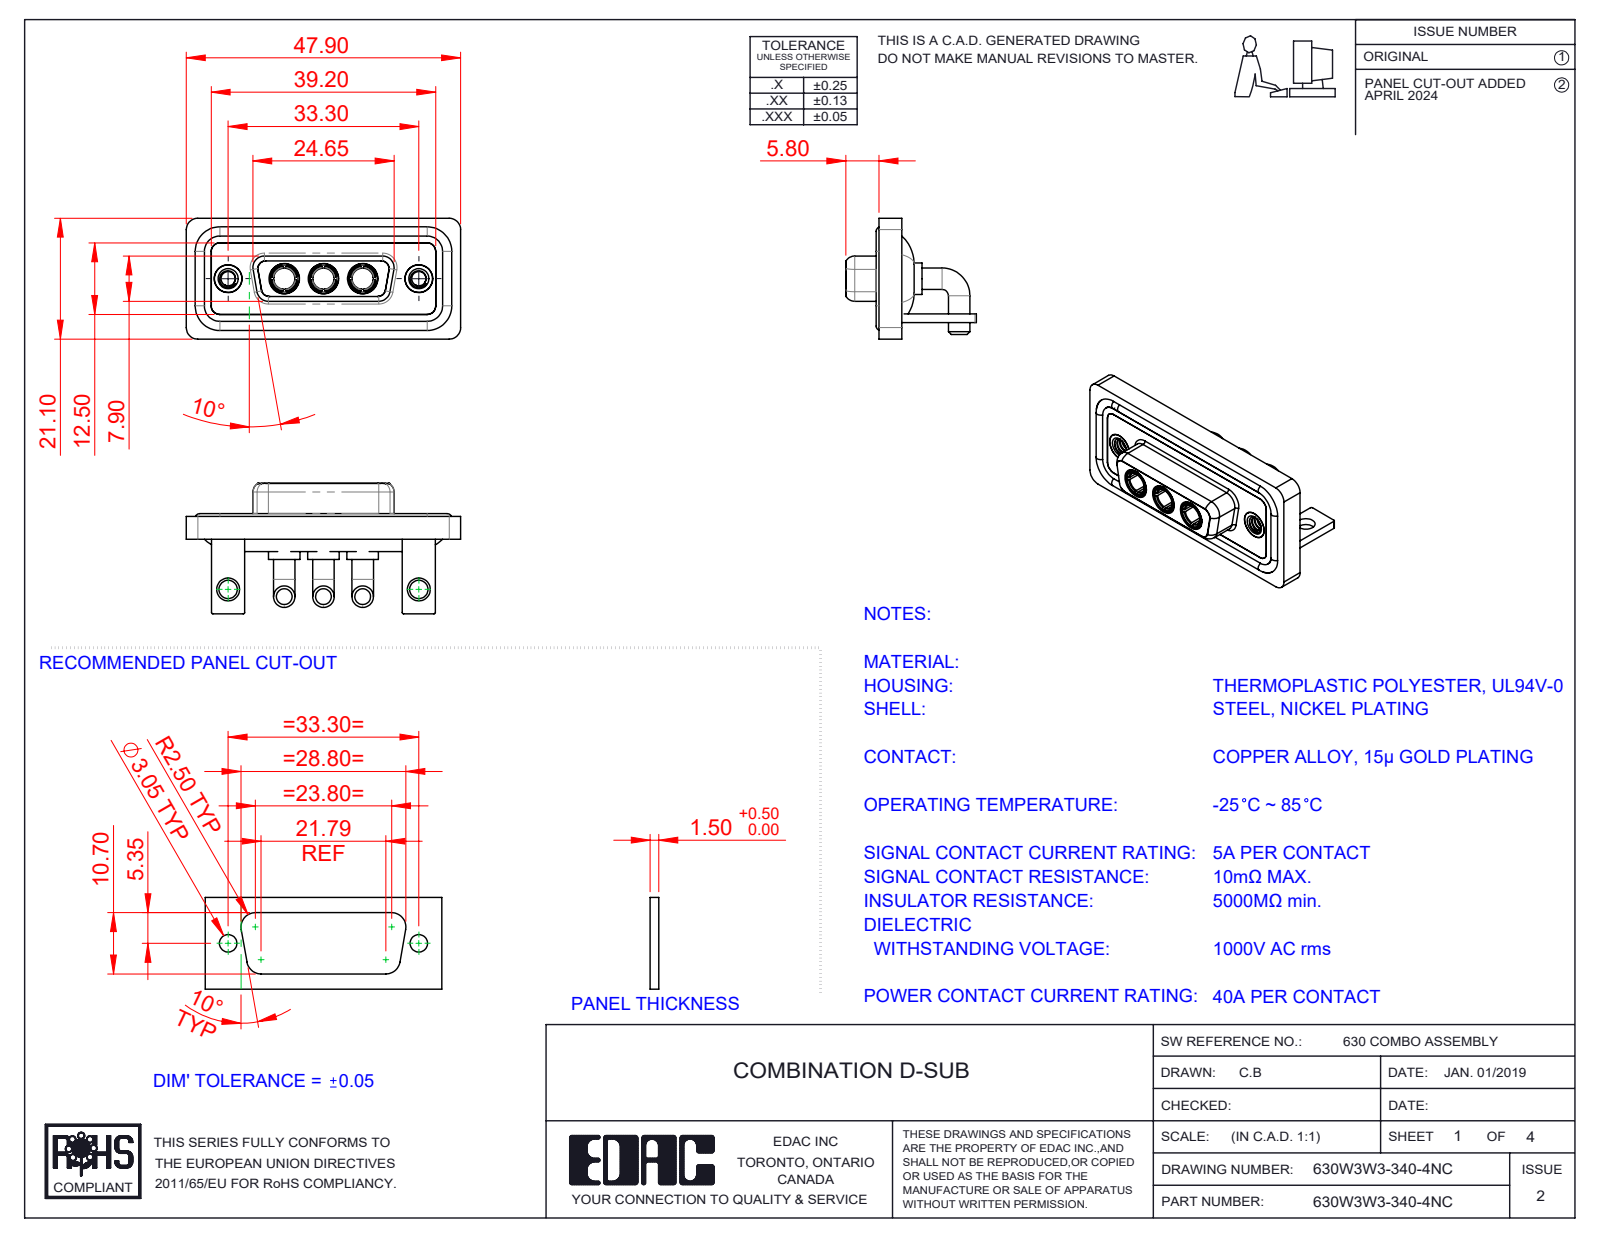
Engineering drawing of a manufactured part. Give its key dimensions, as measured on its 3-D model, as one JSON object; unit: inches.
{"part_name": "630Combo Housing_3W3; 630Combo Threaded Rivet_A; Power Socket_40A RA; 630W3W3-340-4NC (+4 more)", "step_written_by": "SolidWorks 2023 (CONFIG_CONTROL_DESIGN)", "units": "inches", "bodies": {"solids": 15, "faces": 662, "planar": 212, "cylindrical": 285, "other": 165}, "overall_size": [1.886, 0.898, 0.831], "volume_in3": 0.412, "surface_area_in2": 16.81, "round_holes": [[0.191, 5], [0.146, 3], [0.209, 3], [0.098, 2], [0.126, 2], [0.157, 2], [0.159, 2], [0.197, 2]], "round_bosses_or_shafts": [[0.148, 6], [0.063, 4], [0.217, 3], [0.205, 3], [0.195, 3], [0.187, 3], [0.195, 2], [0.189, 2]], "partial_cylinders_radius": [[0.079, 21], [0.059, 18], [0.01, 16], [0.053, 12], [0.063, 8], [0.02, 5], [0.024, 4], [0.026, 4]], "face_to_face_distances": [0.016, 0.114, 0.059, 0.071, 0.146, 0.043, 0.161, 0.063, 0.098, 0.055], "hole_center_spacings": [0.27, 0.386, 0.656, 0.925, 1.311, 0.539]}
